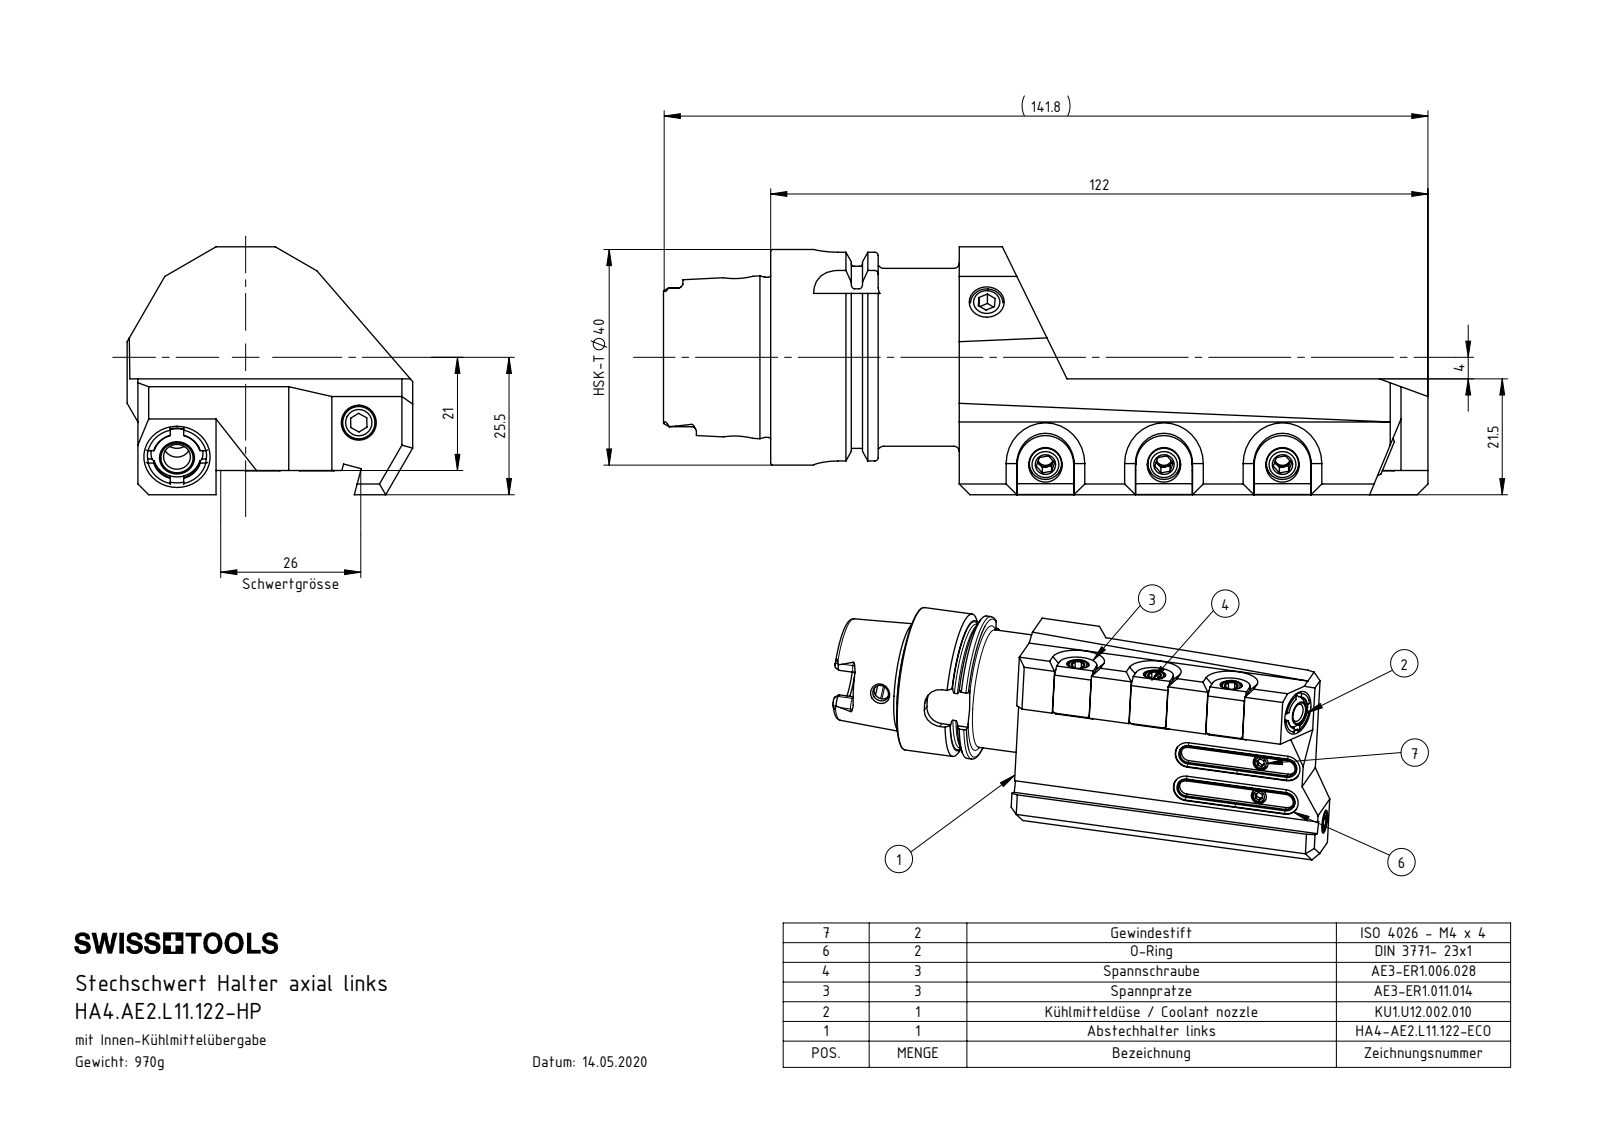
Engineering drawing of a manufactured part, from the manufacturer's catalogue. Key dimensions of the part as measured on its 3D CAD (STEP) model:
Part name (STEP PRODUCT): AE3-ER1.011.014_A; KU1-U12.003.010_B; DIN 3771 - 23x1_vorgespannt 28.5mm Nutlnge; DIN 3771 - 8x1.5 (+7 more)
STEP written by: SolidWorks 2017 (CONFIG_CONTROL_DESIGN)
Units: millimetres
Bodies: 17 solids, 477 faces (262 planar, 98 cylindrical, 117 other)
Overall size (bounding box): 141.9 × 53 × 46
Volume: 124 034 mm³ · Surface area: 37 311 mm²
Round holes (diameter × count): ⌀5 ×9, ⌀3 ×3, ⌀5.5 ×3, ⌀6.2 ×3, ⌀3.3 ×2, ⌀10 ×2, ⌀11 ×2, ⌀4.6 ×1, ⌀12.5 ×1, ⌀21 ×1, ⌀25.5 ×1
Round bosses / shafts (diameter × count): ⌀6 ×6, ⌀1 ×4, ⌀4.5 ×3, ⌀4 ×2, ⌀40 ×1, ⌀34.75 ×1, ⌀33 ×1, ⌀29.71 ×1
Partial cylindrical surfaces — rounded edges, fillets, slot ends (radius × count): R0.9 ×6, R1.88 ×4, R2.25 ×4, R2.65 ×4, R3.65 ×4, R4.5 ×4, R5.25 ×3, R5.3 ×3
Main face-to-face distances: 17, 4.5, 21.5, 22, 51, 10.55, 35, 21.45, 44, 4.45
Hole centre spacings: 22, 10, 24.25, 44, 98.25, 110.55, 111.29
